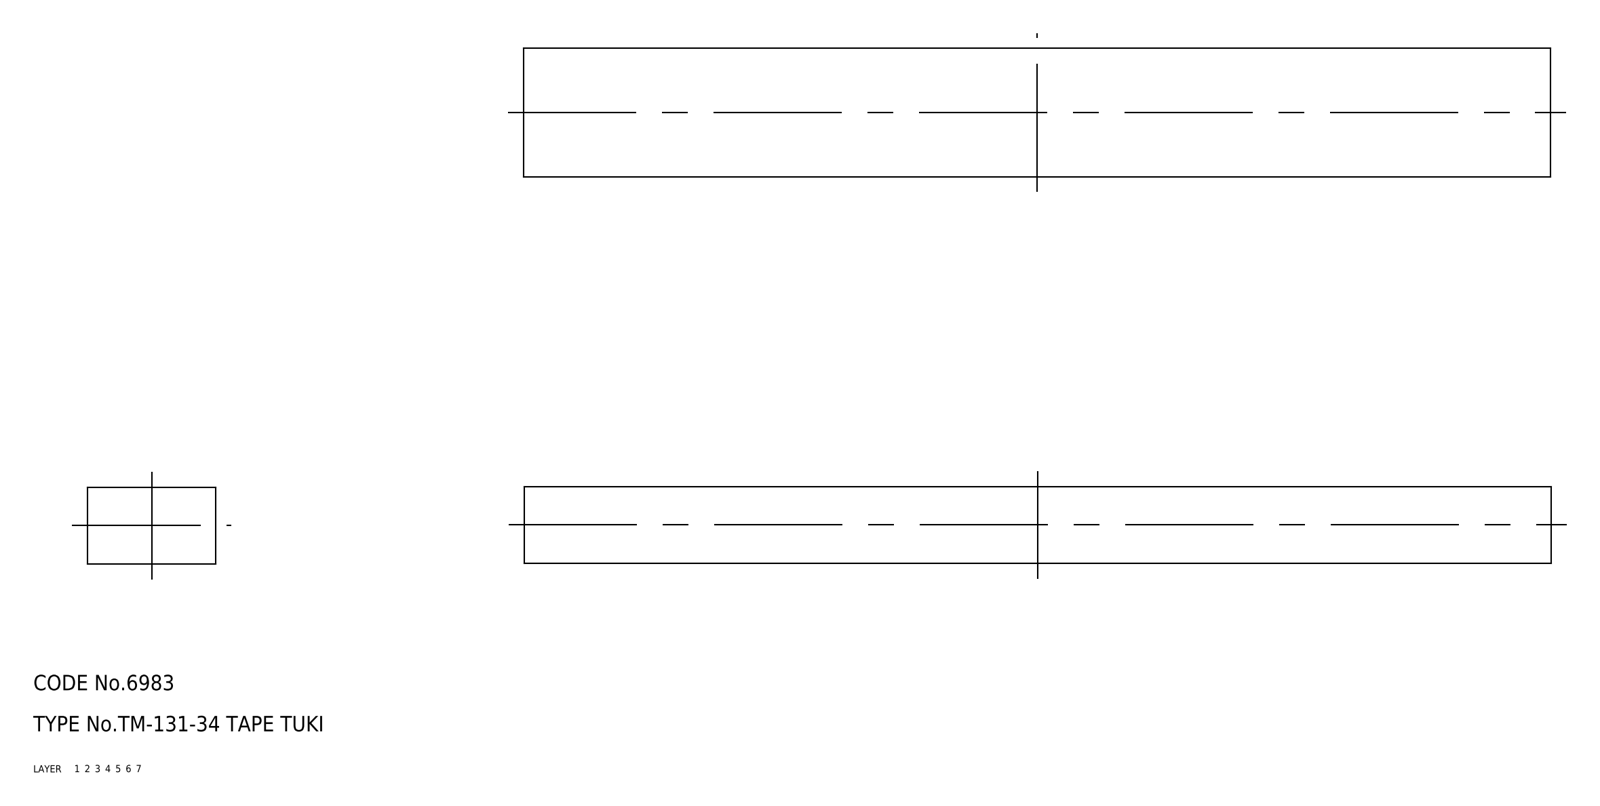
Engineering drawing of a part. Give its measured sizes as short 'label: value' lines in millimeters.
name: rubber foam
written by: CADfix (AUTOMOTIVE_DESIGN)
unit: mm
bodies: 1 solid, 6 faces (0 planar, 0 cylindrical, 6 other)
size: 200 × 25 × 15
volume: 75 000 mm³; area: 16 750 mm²
